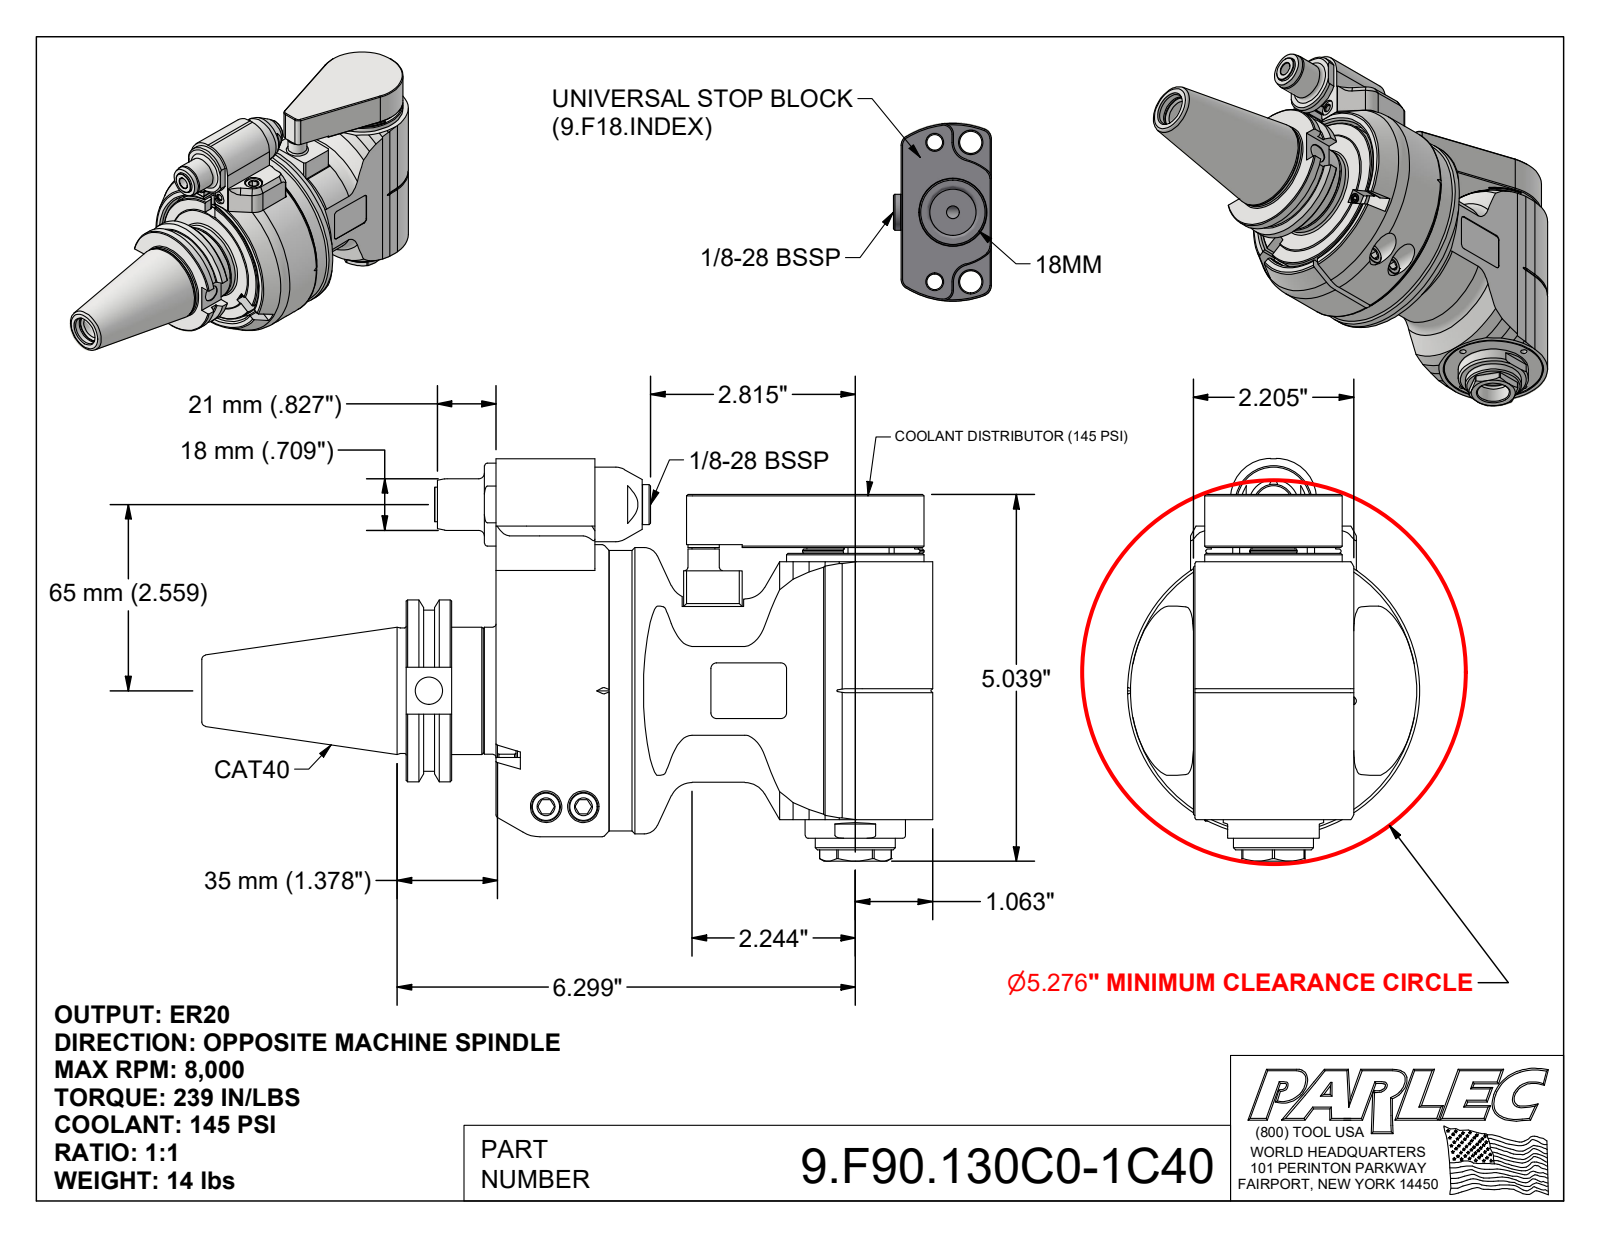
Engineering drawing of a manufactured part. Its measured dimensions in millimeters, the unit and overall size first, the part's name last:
Units: millimetres
Overall size (bounding box): 255.2 × 140.5 × 102
Round holes (diameter × count): ⌀3.2 ×10, ⌀5 ×7, ⌀4.2 ×6, ⌀3.3 ×4, ⌀6 ×3, ⌀6.5 ×3, ⌀8 ×3, ⌀20.5 ×3, ⌀2.6 ×2, ⌀6.8 ×2, ⌀10.4 ×2, ⌀11 ×2
Round bosses / shafts (diameter × count): ⌀10 ×5, ⌀6 ×4, ⌀4 ×4, ⌀22 ×2, ⌀18 ×2, ⌀12 ×2, ⌀8 ×2, ⌀5 ×2
Partial cylindrical surfaces — rounded edges, fillets, slot ends (radius × count): R1 ×14, R2 ×12, R3 ×8, R4 ×4, R0.4 ×2, R0.5 ×2, R8 ×2, R14 ×2
Main face-to-face distances: 32, 0.5, 26.5, 8, 7.5, 7, 1, 8.5, 3, 39.5
Hole centre spacings: 21.5, 8.3, 11.7, 30.4, 37.2, 7, 11.1, 12
Volume: 1 031 000 mm³ · Surface area: 178 900 mm²
Bodies: 27 solids, 847 faces (355 planar, 235 cylindrical, 257 other)
Part name (STEP PRODUCT): 9.F90.130C0-1C40; F901300-0B1000; 9GA11C_446_ASM; 9FA636000 (+8 more)
STEP written by: Autodesk Inventor 2022 (AUTOMOTIVE_DESIGN)
